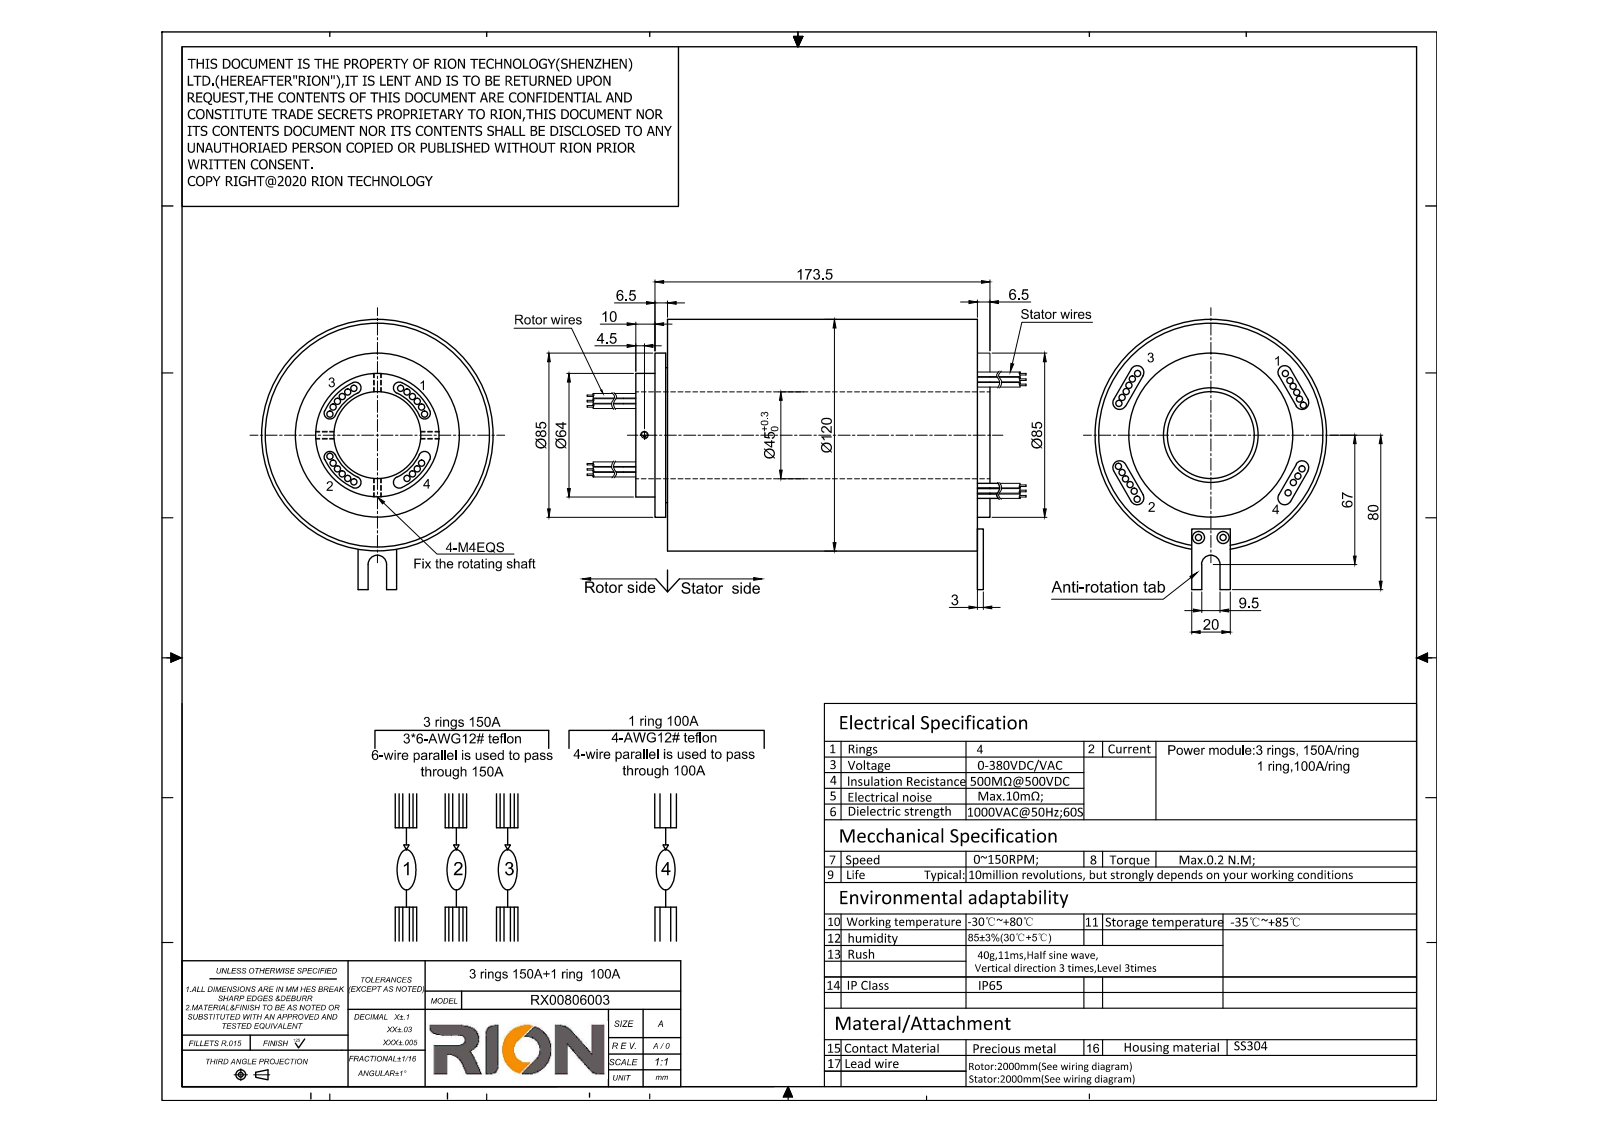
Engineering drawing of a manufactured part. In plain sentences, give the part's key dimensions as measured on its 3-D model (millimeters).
The part is named "RX00806003--RT045-P03150-P01100-IP65". Its 3-D file was written by "SolidWorks 2014 (CONFIG_CONTROL_DESIGN)". It is 1 solid with 228 faces: 75 planar, 145 cylindrical and 8 other. Overall it measures 217 by 140 by 120 millimeters. Its volume is 1 635 000 cubic millimeters and its surface area 125 374 square millimeters. Round holes: 2 of diameter 3.2, 2 of diameter 3.3, 1 of diameter 45. Round bosses or shafts: 44 of diameter 3.2, 1 of diameter 120, 1 of diameter 85, 1 of diameter 70, 1 of diameter 64. Partial cylindrical surfaces (rounded edges, fillets, slot ends): 16 of radius 3, 1 of radius 4.75, 1 of radius 24, 1 of radius 30. The main face-to-face distances are 6.5, 167, 160.5, 173.5, 5.5, 1, 161.5, 168, 10, 15.5. The hole center spacings are 53.38, 12.7.
